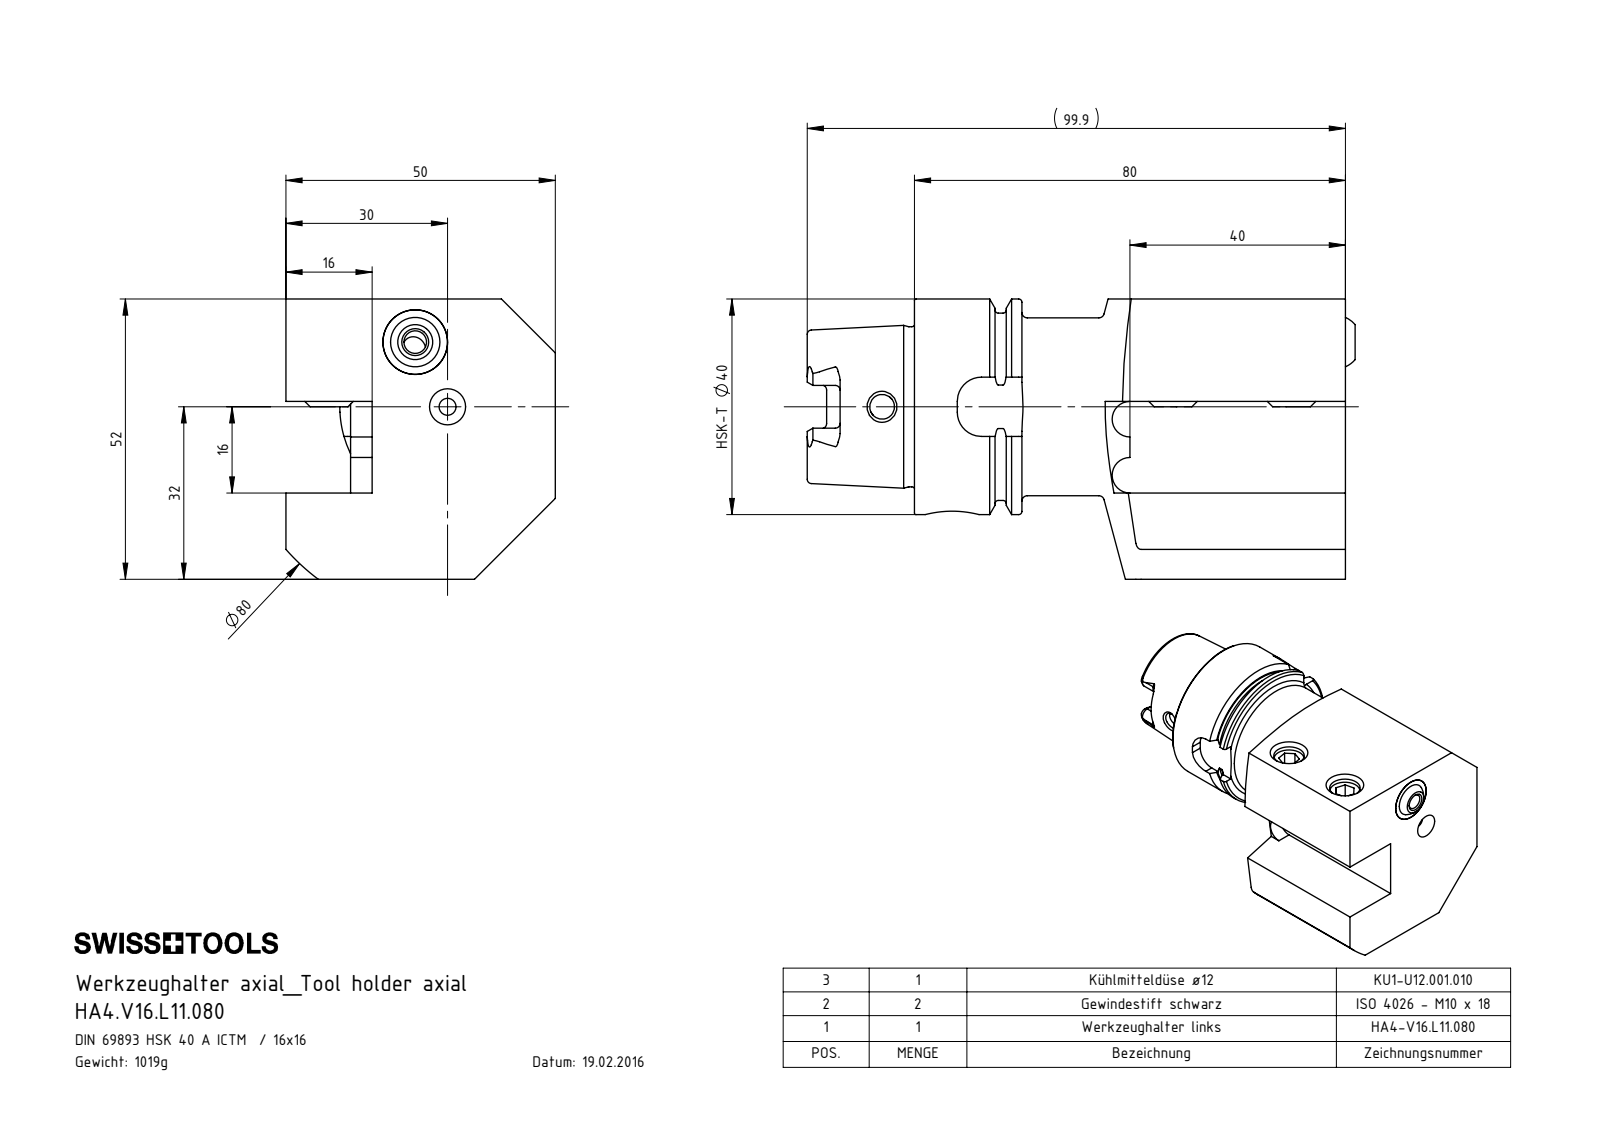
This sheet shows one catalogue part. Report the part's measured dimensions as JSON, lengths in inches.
{"part_name": "HA4.V16.L11.080; HA4-V16.L11.080_A_Fertigbearbeitung; KU1-U12.001.010_1; KU1-U12.001.010 (+2 more)", "step_written_by": "SolidWorks 2017 (AUTOMOTIVE_DESIGN)", "units": "inches", "bodies": {"solids": 5, "faces": 185, "planar": 80, "cylindrical": 45, "other": 60}, "overall_size": [4.004, 2.047, 1.969], "volume_in3": 7.939, "surface_area_in2": 42.6, "round_holes": [[0.165, 2], [0.335, 2], [0.124, 1], [0.181, 1], [0.197, 1], [0.276, 1], [0.394, 1], [0.433, 1], [0.472, 1], [0.492, 1], [0.827, 1], [1.004, 1]], "round_bosses_or_shafts": [[0.394, 2], [1.575, 1], [1.368, 1], [1.299, 1], [1.17, 1]], "partial_cylinders_radius": [[0.035, 6], [0.074, 4], [0.177, 4], [0.13, 2], [1.575, 1]], "face_to_face_distances": [0.63, 1.969, 2.047, 1.339, 1.417, 0.669, 1.299, 0.748, 3.15, 0.472], "hole_center_spacings": [0.528, 0.866, 1.832, 2.627]}
